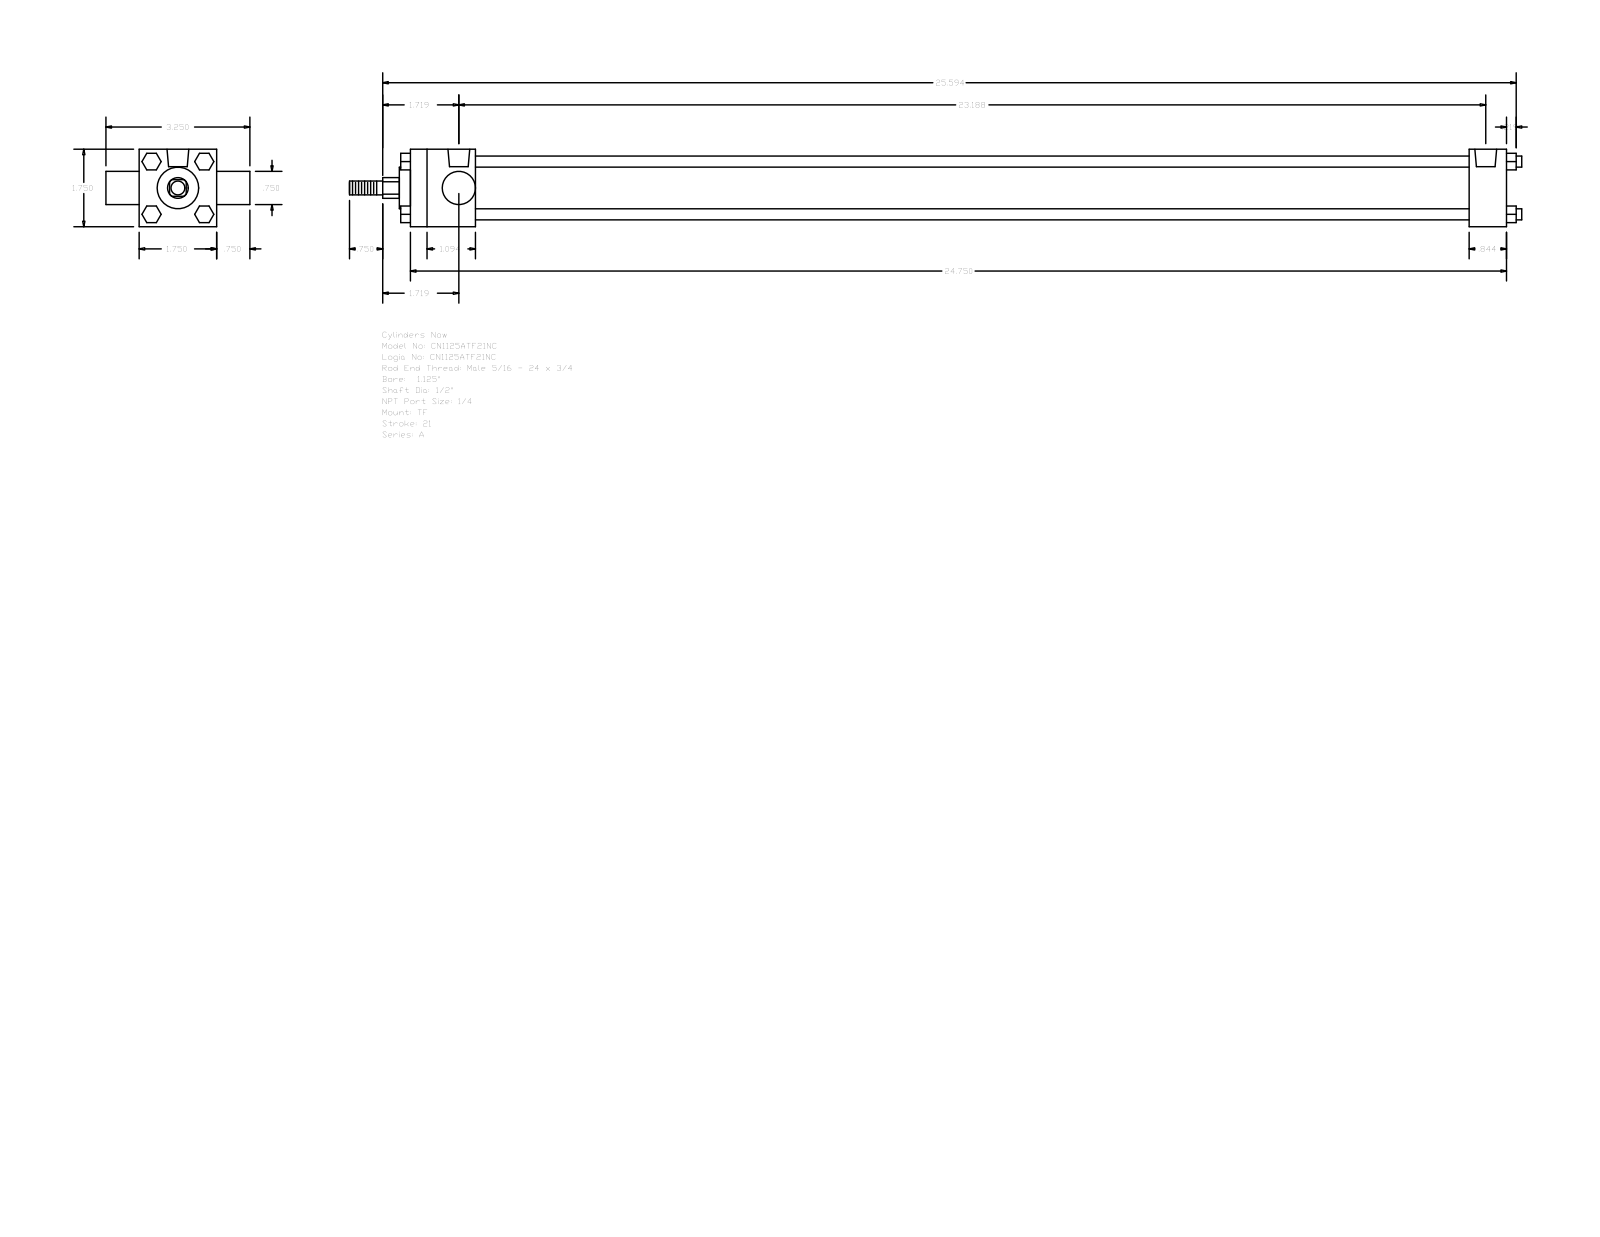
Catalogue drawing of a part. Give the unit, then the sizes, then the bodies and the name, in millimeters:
Units: millimetres
Overall size (bounding box): 672.31 × 82.55 × 44.45
Round holes (diameter × count): ⌀5.56 ×3, ⌀12.49 ×2
Round bosses / shafts (diameter × count): ⌀6.35 ×4, ⌀31.88 ×1, ⌀23.81 ×1, ⌀19.05 ×1, ⌀12.7 ×1, ⌀7.94 ×1
Partial cylindrical surfaces — rounded edges, fillets, slot ends (radius × count): R5.94 ×1
Main face-to-face distances: 44.46, 628.64, 607.21, 21.43, 37.3, 569.91, 591.34, 19.04, 63.5, 9.53
Hole centre spacings: 1.58, 1.59, 585.79, 587.37, 587.38, 588.96
Bodies: 0 solids, 120 faces (92 planar, 28 cylindrical, 0 other)
Part name (STEP PRODUCT): A_TF__0112_0.5
STEP written by: GSSL Pune (CONFIG_CONTROL_DESIGN)
